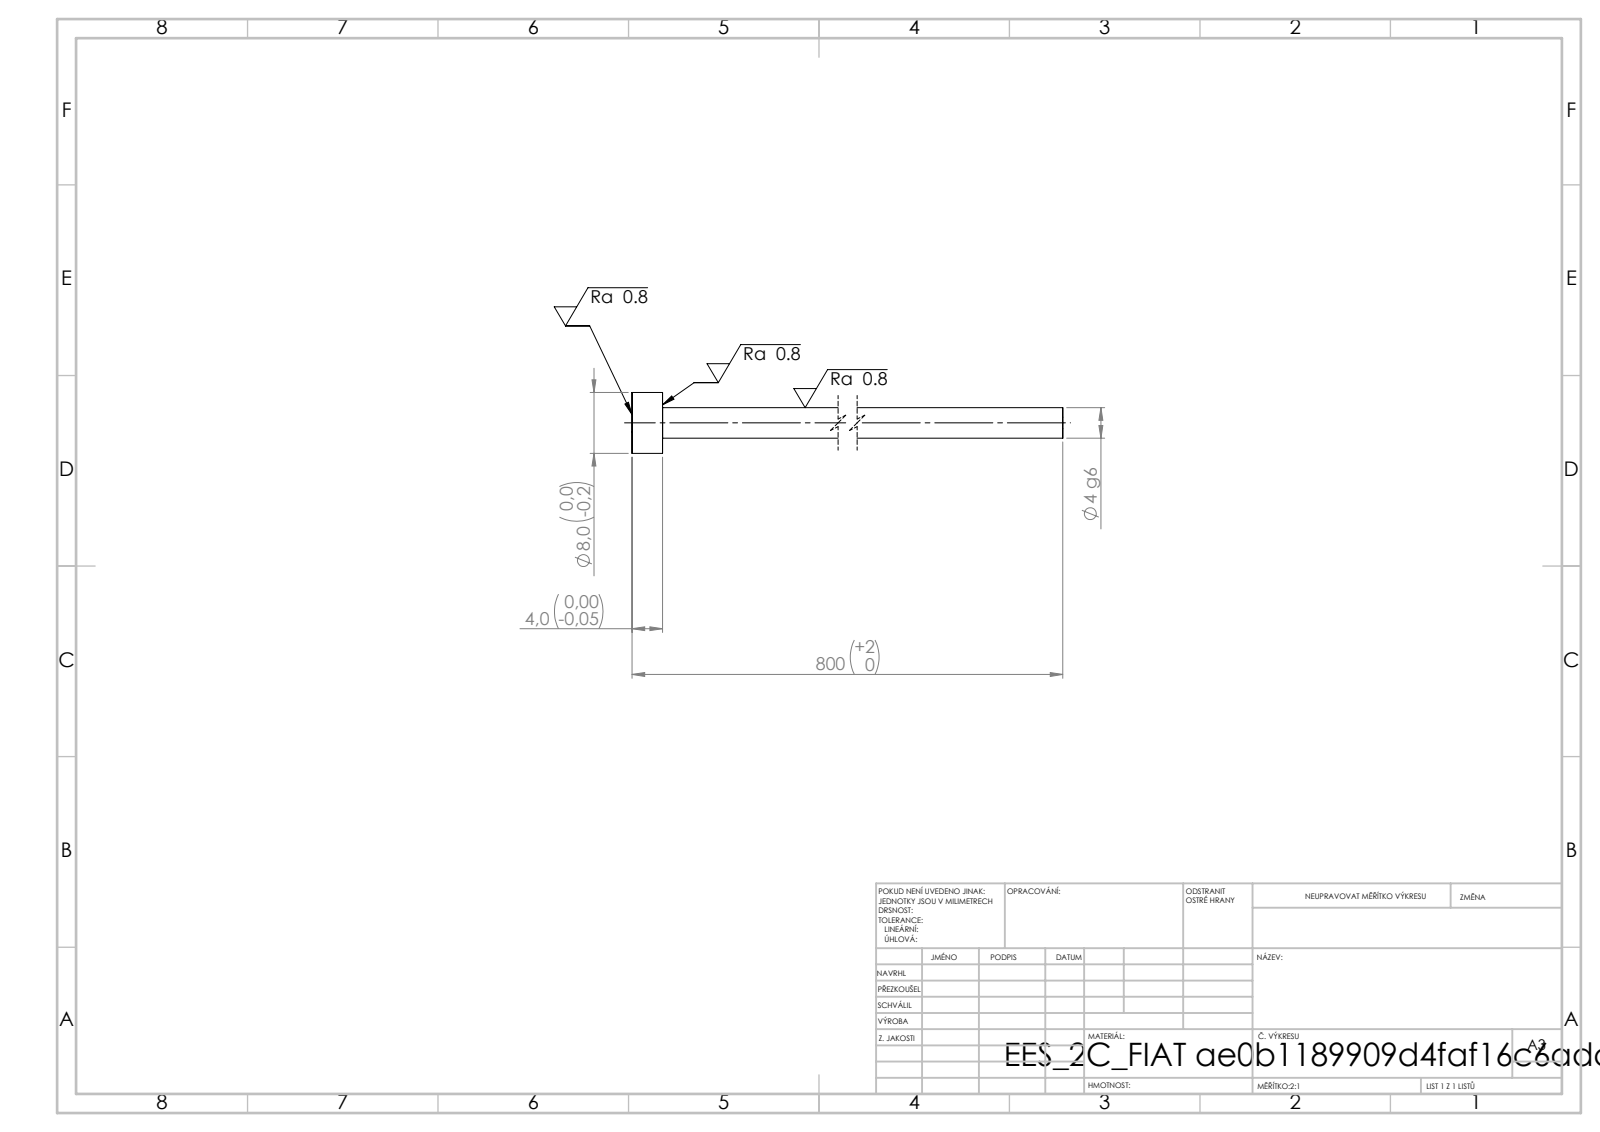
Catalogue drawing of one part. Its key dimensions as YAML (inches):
step_written_by: "SolidWorks 2019 (CONFIG_CONTROL_DESIGN)"
units: inches
bodies: {solids: 1, faces: 7, planar: 3, cylindrical: 4, other: 0}
overall_size: [31.496, 0.315, 0.315]
volume: 0.623
surface_area: 15.82
round_bosses_or_shafts:
  - {diameter: 0.315, count: 1}
  - {diameter: 0.157, count: 1}
face_to_face_distances: [0.157, 31.496, 31.339]
